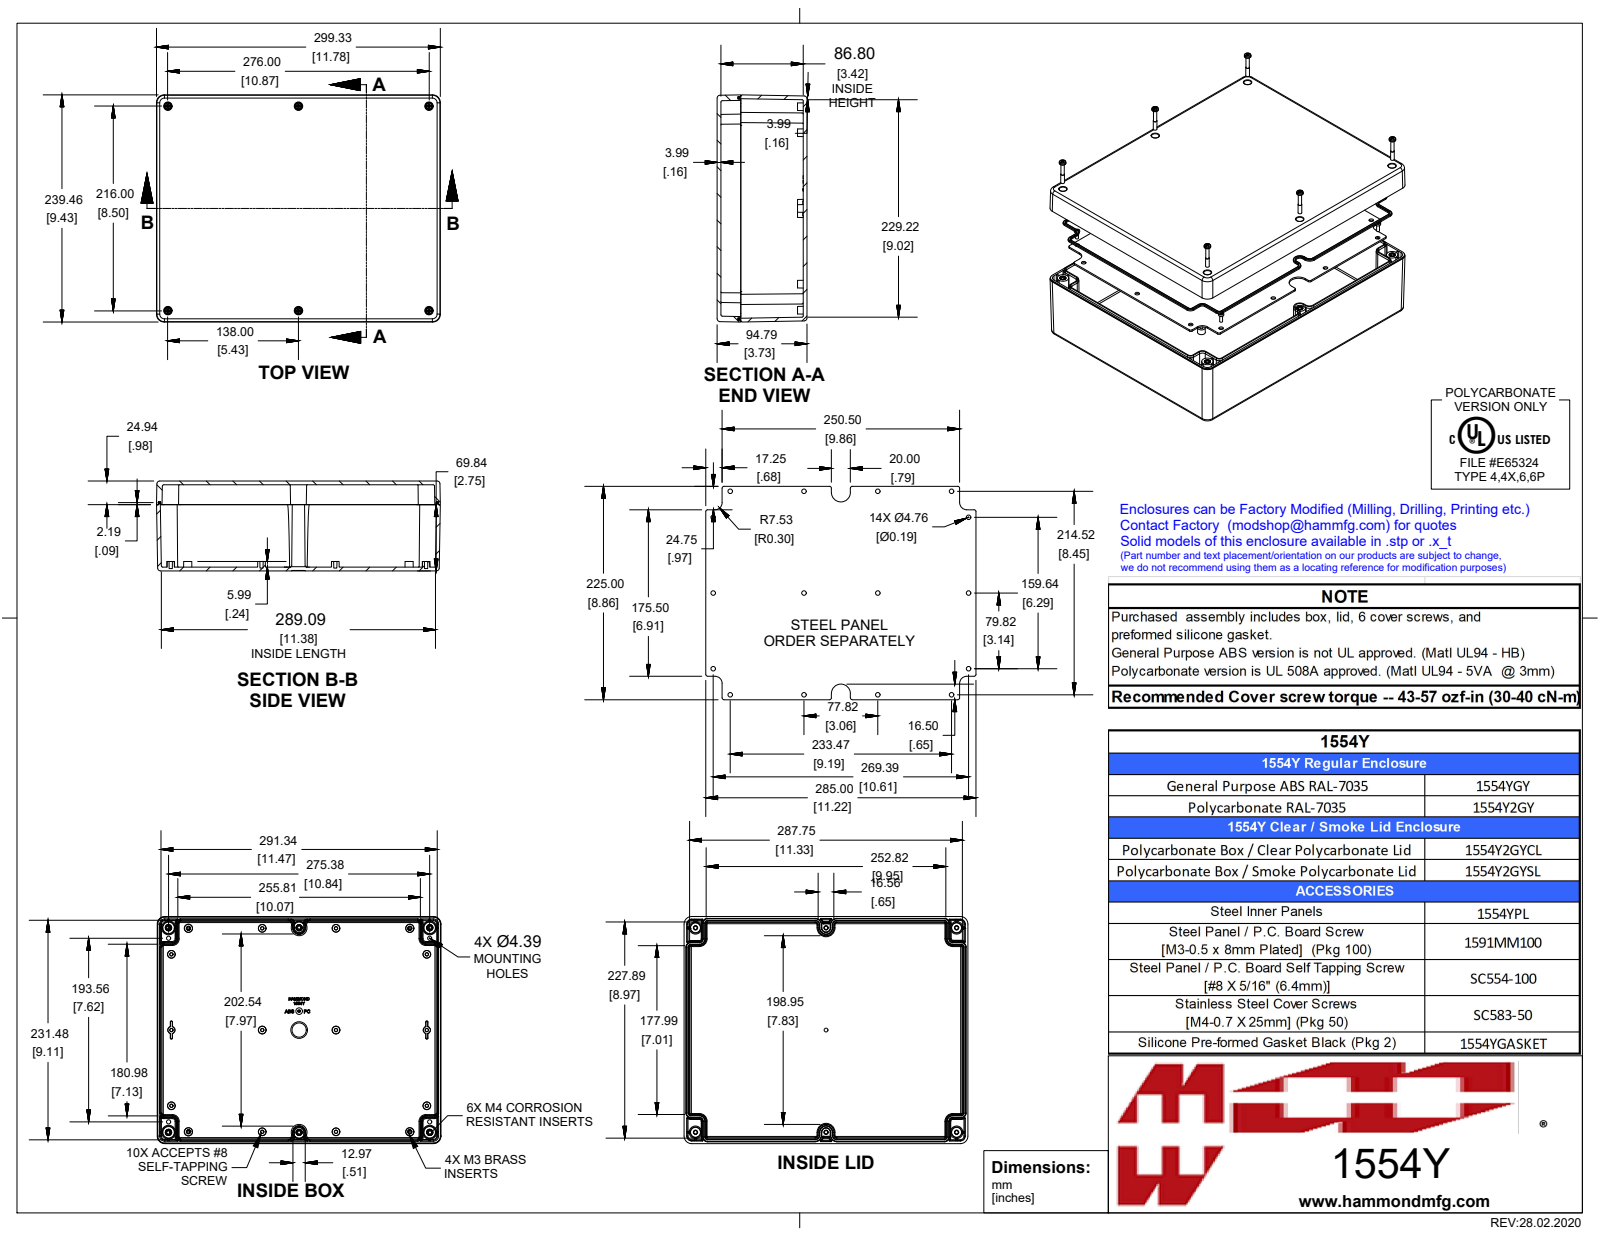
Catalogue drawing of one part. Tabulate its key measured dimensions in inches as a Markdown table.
| quantity | value |
| --- | --- |
| part name | 1554Y2GY |
| STEP written by | SolidWorks 2019 (AUTOMOTIVE_DESIGN) |
| units | inches |
| bodies | 24 solids, 3194 faces (890 planar, 718 cylindrical, 1586 other) |
| overall size | 11.811 × 9.449 × 3.74 |
| volume | 69.09 in³ |
| surface area | 1 067 in² |
| round holes (diameter × count) | 0.187 × 16, 0.128 × 6, 0.142 × 6, 0.097 × 4, 0.276 × 1 |
| round bosses / shafts (diameter × count) | 0.272 × 6, 0.25 × 6, 0.213 × 6, 0.21 × 6, 0.152 × 6, 0.137 × 6, 0.118 × 5, 0.19 × 4 |
| partial cylindrical surfaces (radius × count) | 0.02 × 32, 0.012 × 20, 0.031 × 20, 0.039 × 18, 0.079 × 12, 0.118 × 12, 0.315 × 8, 0.051 × 4 |
| main face-to-face distances | 0.157, 3.583, 3.74, 3.425, 3.346, 0.236, 0.394, 3.189, 0.064, 0.458 |
| hole center spacings | 5.229, 3.071, 9.004, 0.827, 1.109, 1.294, 1.535, 3.15 |
